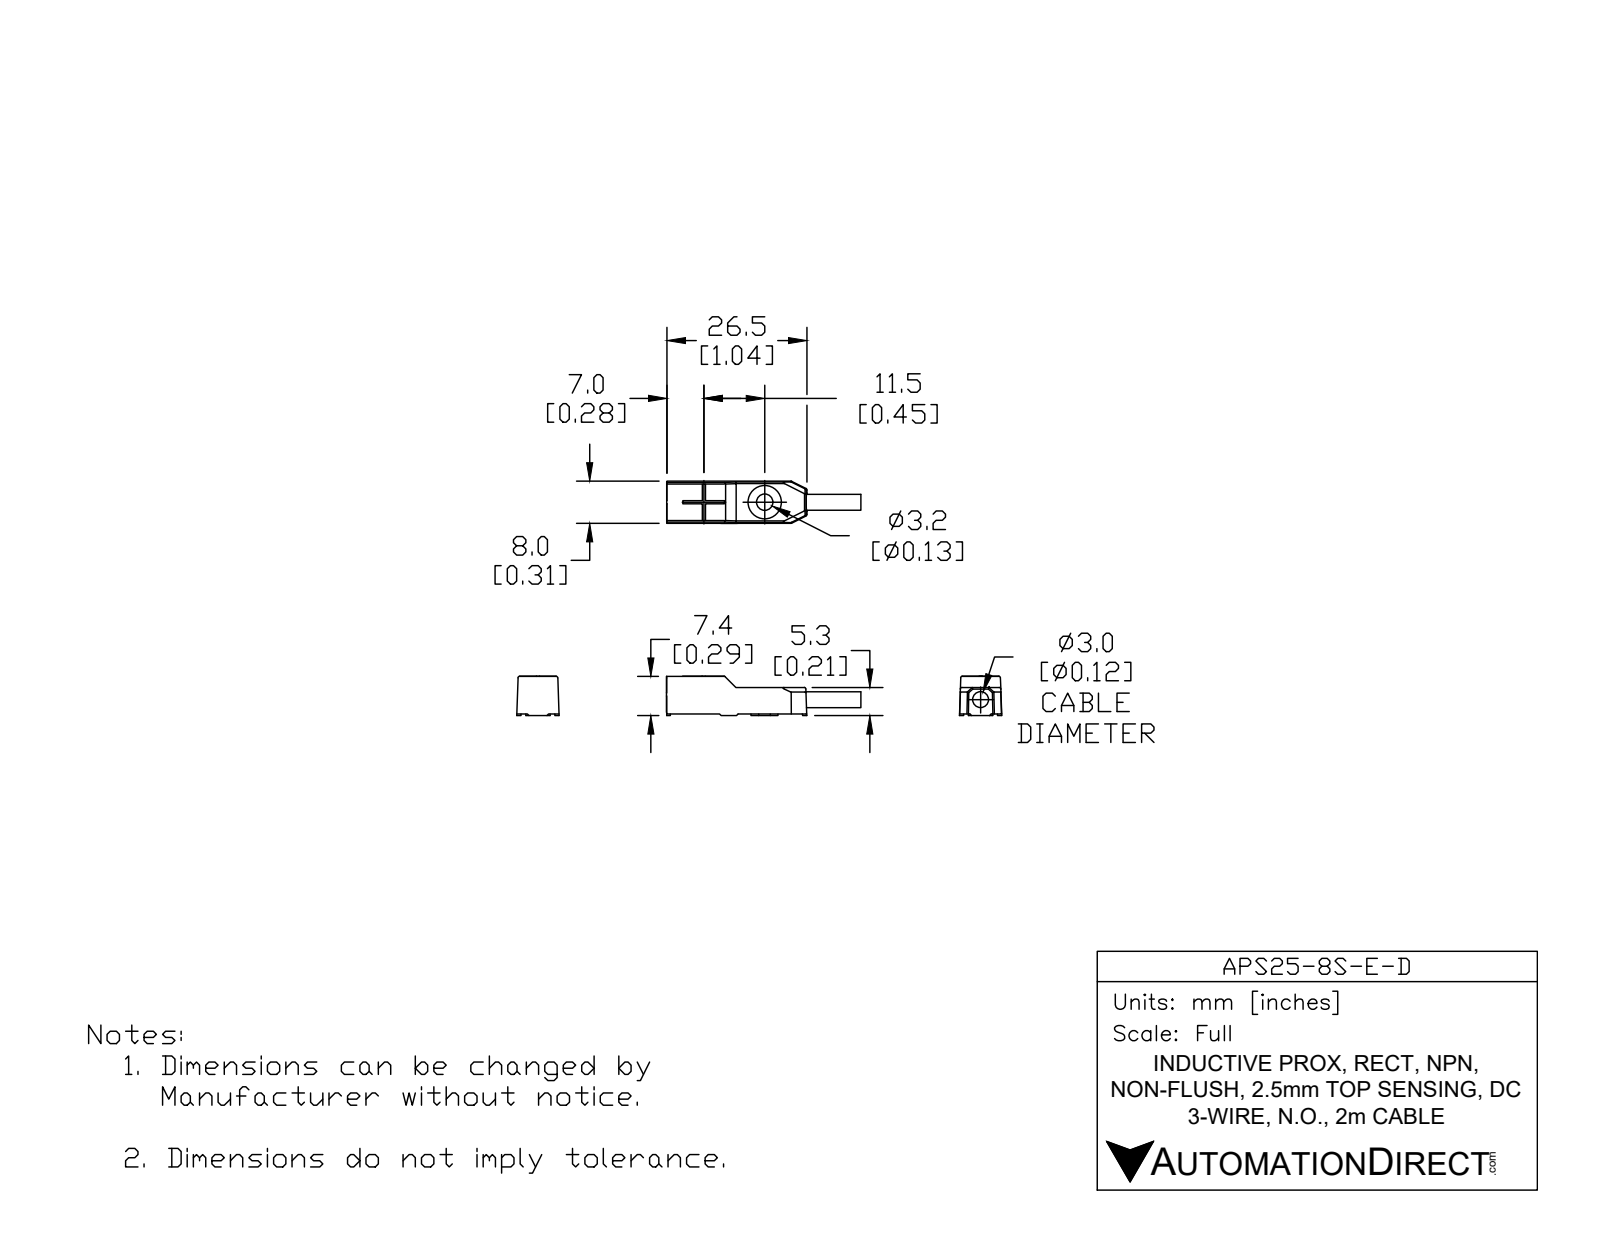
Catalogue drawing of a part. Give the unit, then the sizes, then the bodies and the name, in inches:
Units: inches
Overall size (bounding box): 1.469 × 0.358 × 0.302
Round holes (diameter × count): ⌀0.081 ×1, ⌀0.126 ×1, ⌀0.205 ×1, ⌀0.217 ×1, ⌀0.24 ×1
Round bosses / shafts (diameter × count): ⌀0.123 ×1
Partial cylindrical surfaces — rounded edges, fillets, slot ends (radius × count): R0.005 ×8, R0.02 ×4, R0.113 ×1, R0.17 ×1
Main face-to-face distances: 0.05, 0.224, 0.212, 0.255, 0.305, 0.236, 0.078, 0.205, 0.022, 0.202
Hole centre spacings: 0.629
Volume: 0.058 in³ · Surface area: 3.616 in²
Bodies: 6 solids, 121 faces (90 planar, 31 cylindrical, 0 other)
Part name (STEP PRODUCT): APS25-8S-E-D
STEP written by: SolidWorks 2017 (AUTOMOTIVE_DESIGN)
